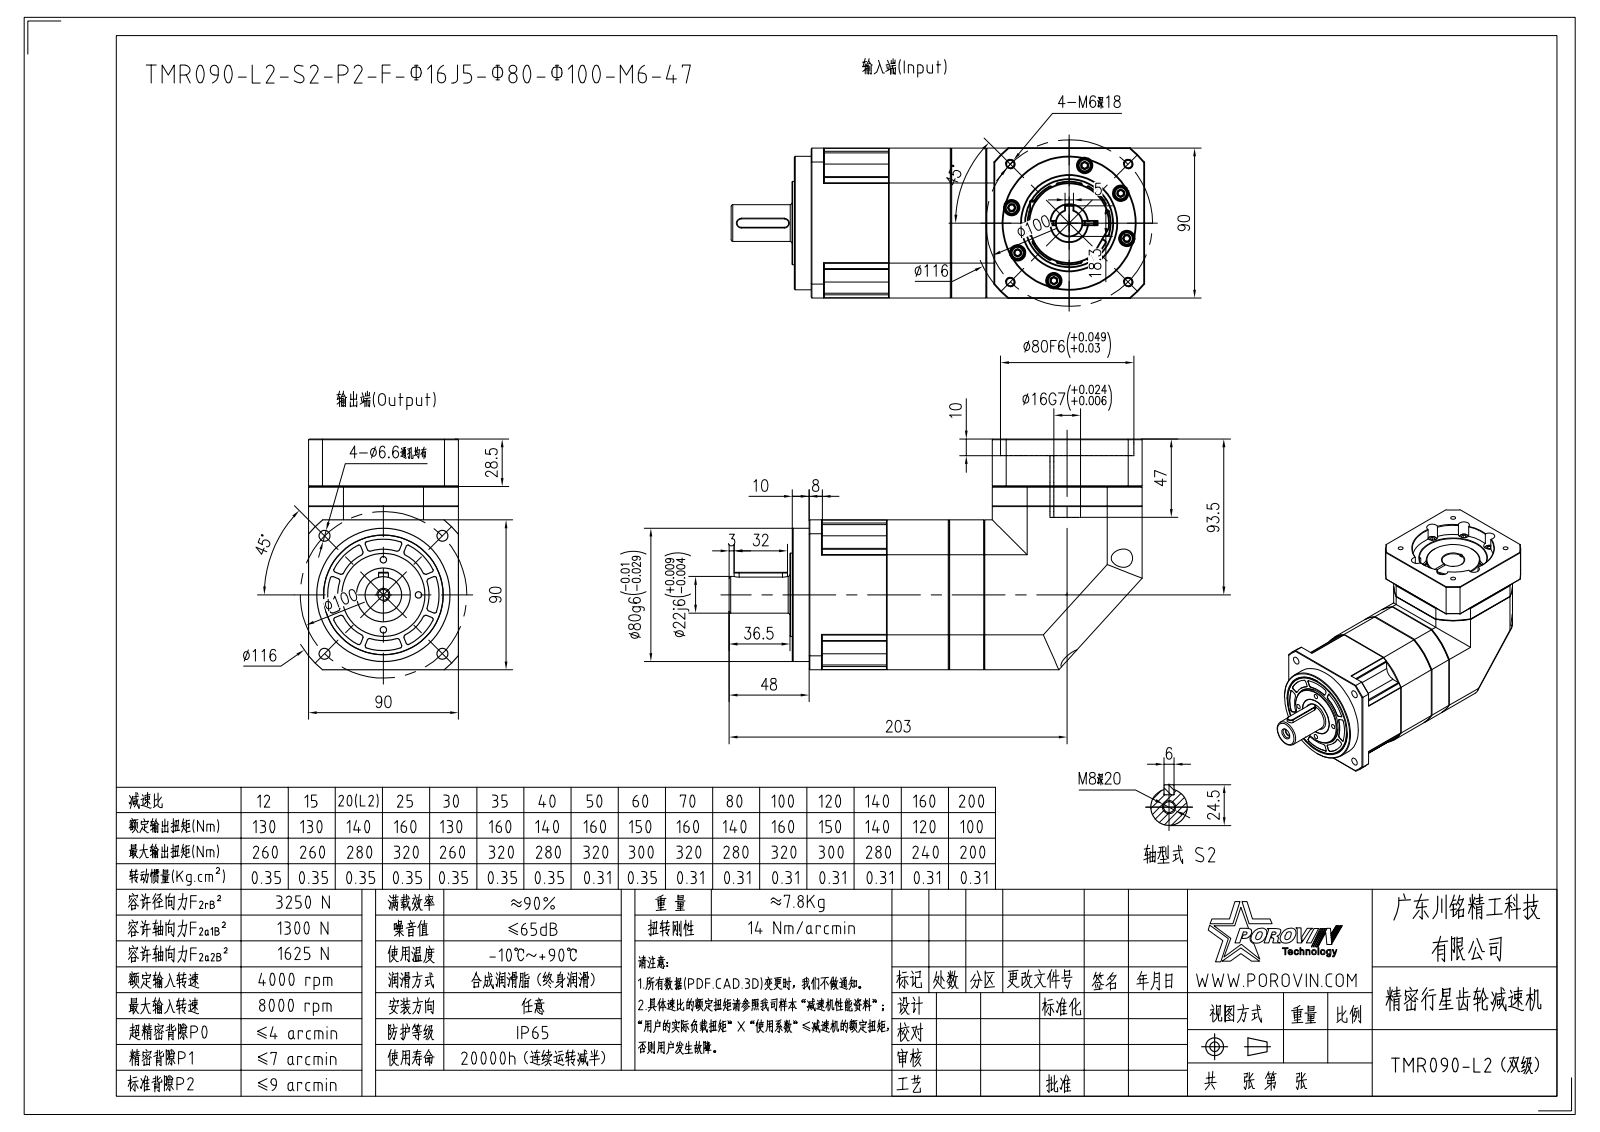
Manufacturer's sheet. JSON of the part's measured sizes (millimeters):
{"part_name": "SPRING_LOCK_WASHERS--NORM-16944; HEXAGON_SOCKET_HEAD_CAP_S-28021; SPRING_LOCK_WASHERS--NORMA-4726; HEXAGON_SOCKET_HEAD_CAP_SC-5274 (+8 more)", "step_written_by": "CREO PARAMETRIC BY PTC INC, 2020053 (CONFIG_CONTROL_DESIGN)", "units": "millimeters", "bodies": {"solids": 43, "faces": 1327, "planar": 532, "cylindrical": 561, "other": 234}, "overall_size": [248, 138.5, 90], "volume_mm3": 1603000, "surface_area_mm2": 238618, "round_holes": [[5.4, 12], [5.5, 12], [9.5, 12], [6.6, 10], [4.2, 7], [5, 5], [6.5, 5], [4, 4], [6.68, 4], [11, 4], [6.8, 1], [8.4, 1]], "round_bosses_or_shafts": [[8.5, 12], [8, 12], [5, 12], [10, 4], [9.88, 4], [6, 4], [80, 1], [78, 1]], "partial_cylinders_radius": [[1, 92], [7.5, 4], [51, 3], [3, 2], [58, 2], [4, 1], [5.25, 1], [20.75, 1]], "face_to_face_distances": [90, 12, 21.5, 21.3, 37.5, 58.8, 59, 110, 10, 98], "hole_center_spacings": [35.75, 27.36, 38.16, 44, 50.01, 66.06, 66.53, 70.72]}
